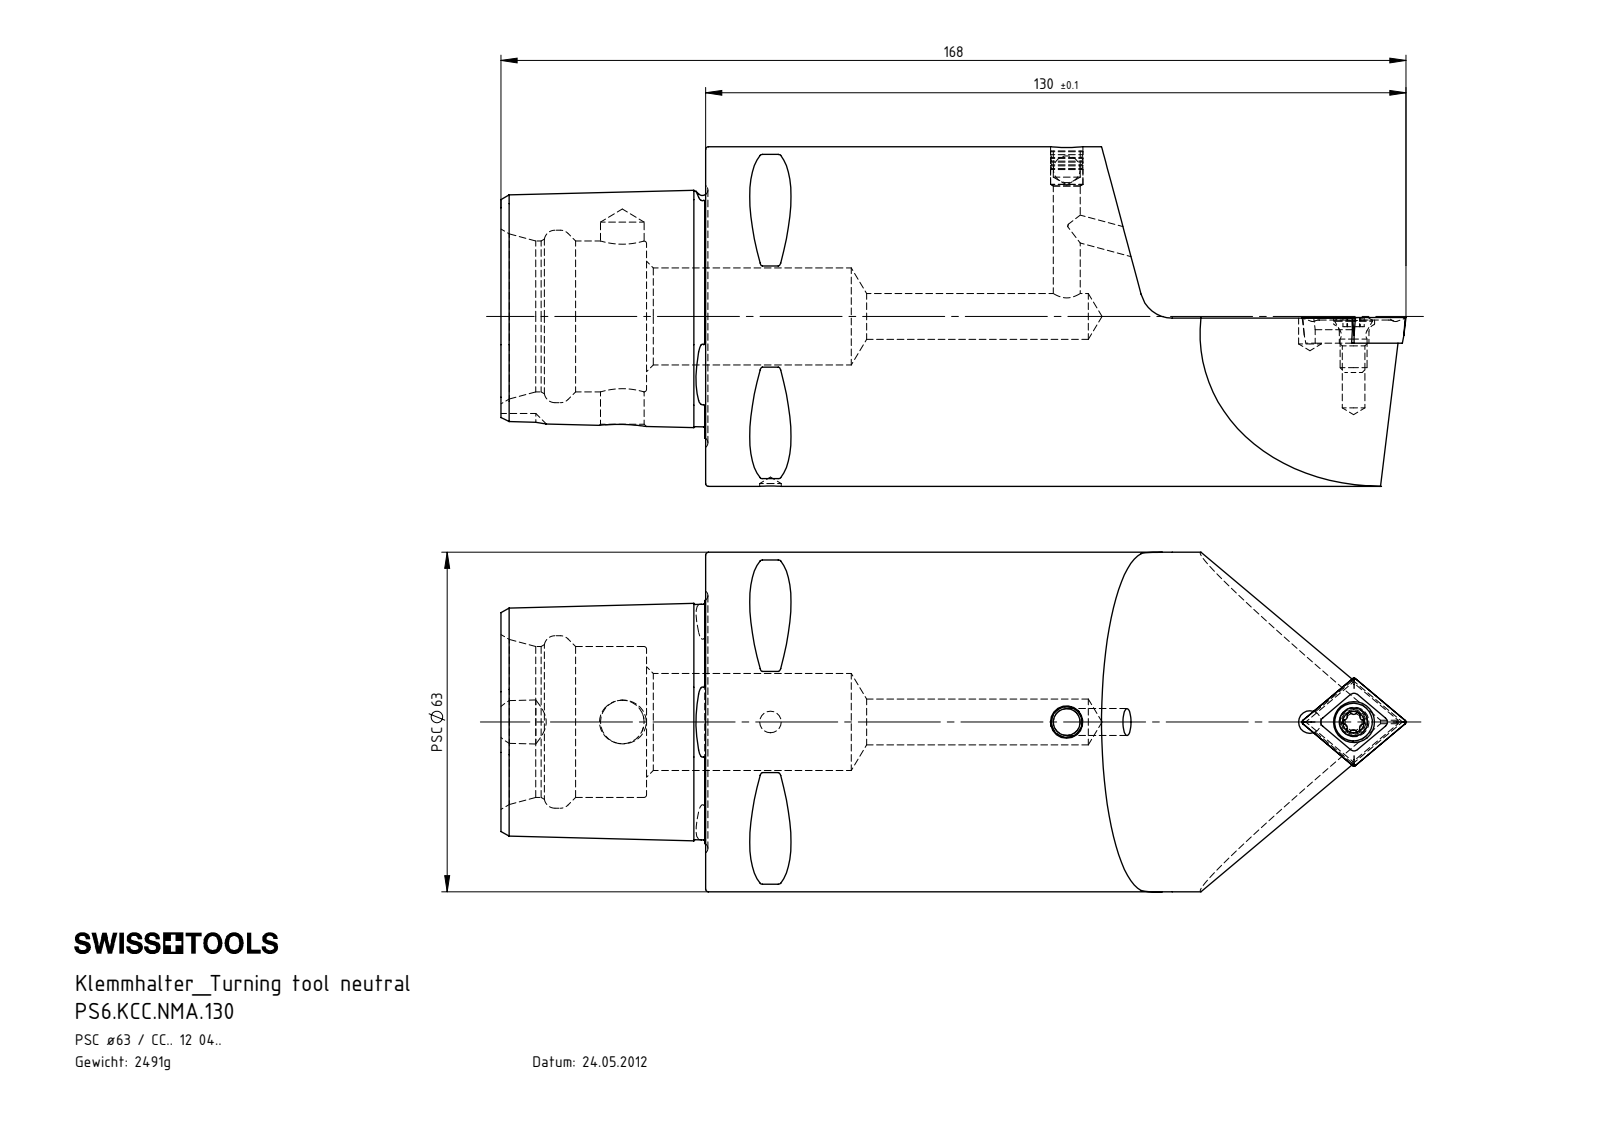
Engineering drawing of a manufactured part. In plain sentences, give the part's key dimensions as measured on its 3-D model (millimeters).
The part is named "CCMT120404; WCC-ER2.001.010_A; KVT_MB_600_060; PS6-KCC.NMA.130_A (+1 more)". Its 3-D file was written by "SolidWorks 2012 (CONFIG_CONTROL_DESIGN)". It is 5 solids with 262 faces: 48 planar, 67 cylindrical and 147 other. Overall it measures 168 by 63 by 63 millimeters. Its volume is 317 357 cubic millimeters and its surface area 39 619 square millimeters. Round holes: 2 of diameter 4.2, 2 of diameter 5, 1 of diameter 4, 1 of diameter 5.5, 1 of diameter 7.6, 1 of diameter 8.1, 1 of diameter 8.5, 1 of diameter 18, 1 of diameter 28, 1 of diameter 32. Round bosses or shafts: 1 of diameter 63, 1 of diameter 7, 1 of diameter 6, 1 of diameter 5. Partial cylindrical surfaces (rounded edges, fillets, slot ends): 8 of radius 0.5, 6 of radius 0.39, 5 of radius 0.69, 2 of radius 6, 1 of radius 0.69. The main face-to-face distances are 38, 24.88, 27, 11, 4.66, 55.8, 37.8, 10.8, 4.76, 29.16. The hole center spacings are 8.1, 8.2, 27.5, 45.14, 53.24, 53.34, 55, 82.5.
